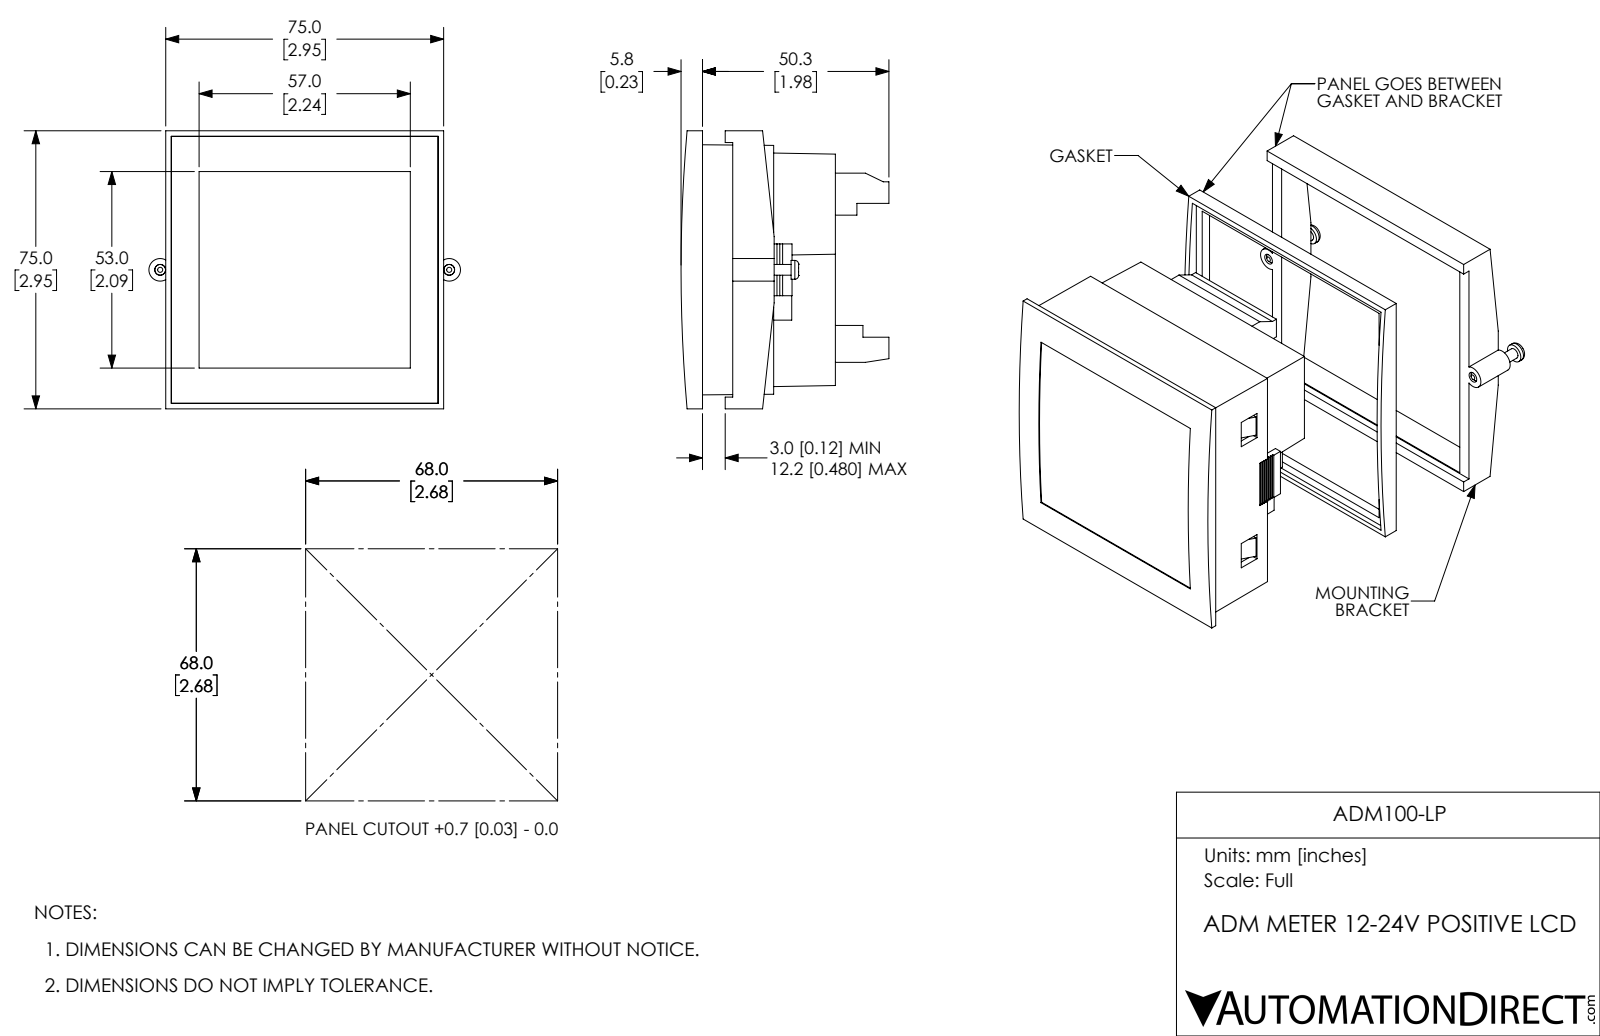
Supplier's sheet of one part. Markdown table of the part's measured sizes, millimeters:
| quantity | value |
| --- | --- |
| part name | ADM100-LP |
| STEP written by | SolidWorks 2017 (AUTOMOTIVE_DESIGN) |
| units | millimeters |
| bodies | 23 solids, 419 faces (335 planar, 76 cylindrical, 8 other) |
| overall size | 84.1 × 75 × 56.1 |
| volume | 156 700 mm³ |
| surface area | 58 480 mm² |
| round holes (diameter × count) | 3.8 × 13, 2.9 × 2 |
| round bosses / shafts (diameter × count) | 3.8 × 13, 5.1 × 2, 2.9 × 2 |
| partial cylindrical surfaces (radius × count) | 3 × 2, 432.7 × 2 |
| main face-to-face distances | 1.9, 7.7, 6, 69, 67.5, 2.3, 3.8, 71.2, 65.6, 29 |
| hole center spacings | 42, 5.1, 42.6, 10.2, 43.8, 15.2, 45.5, 20.3 |
